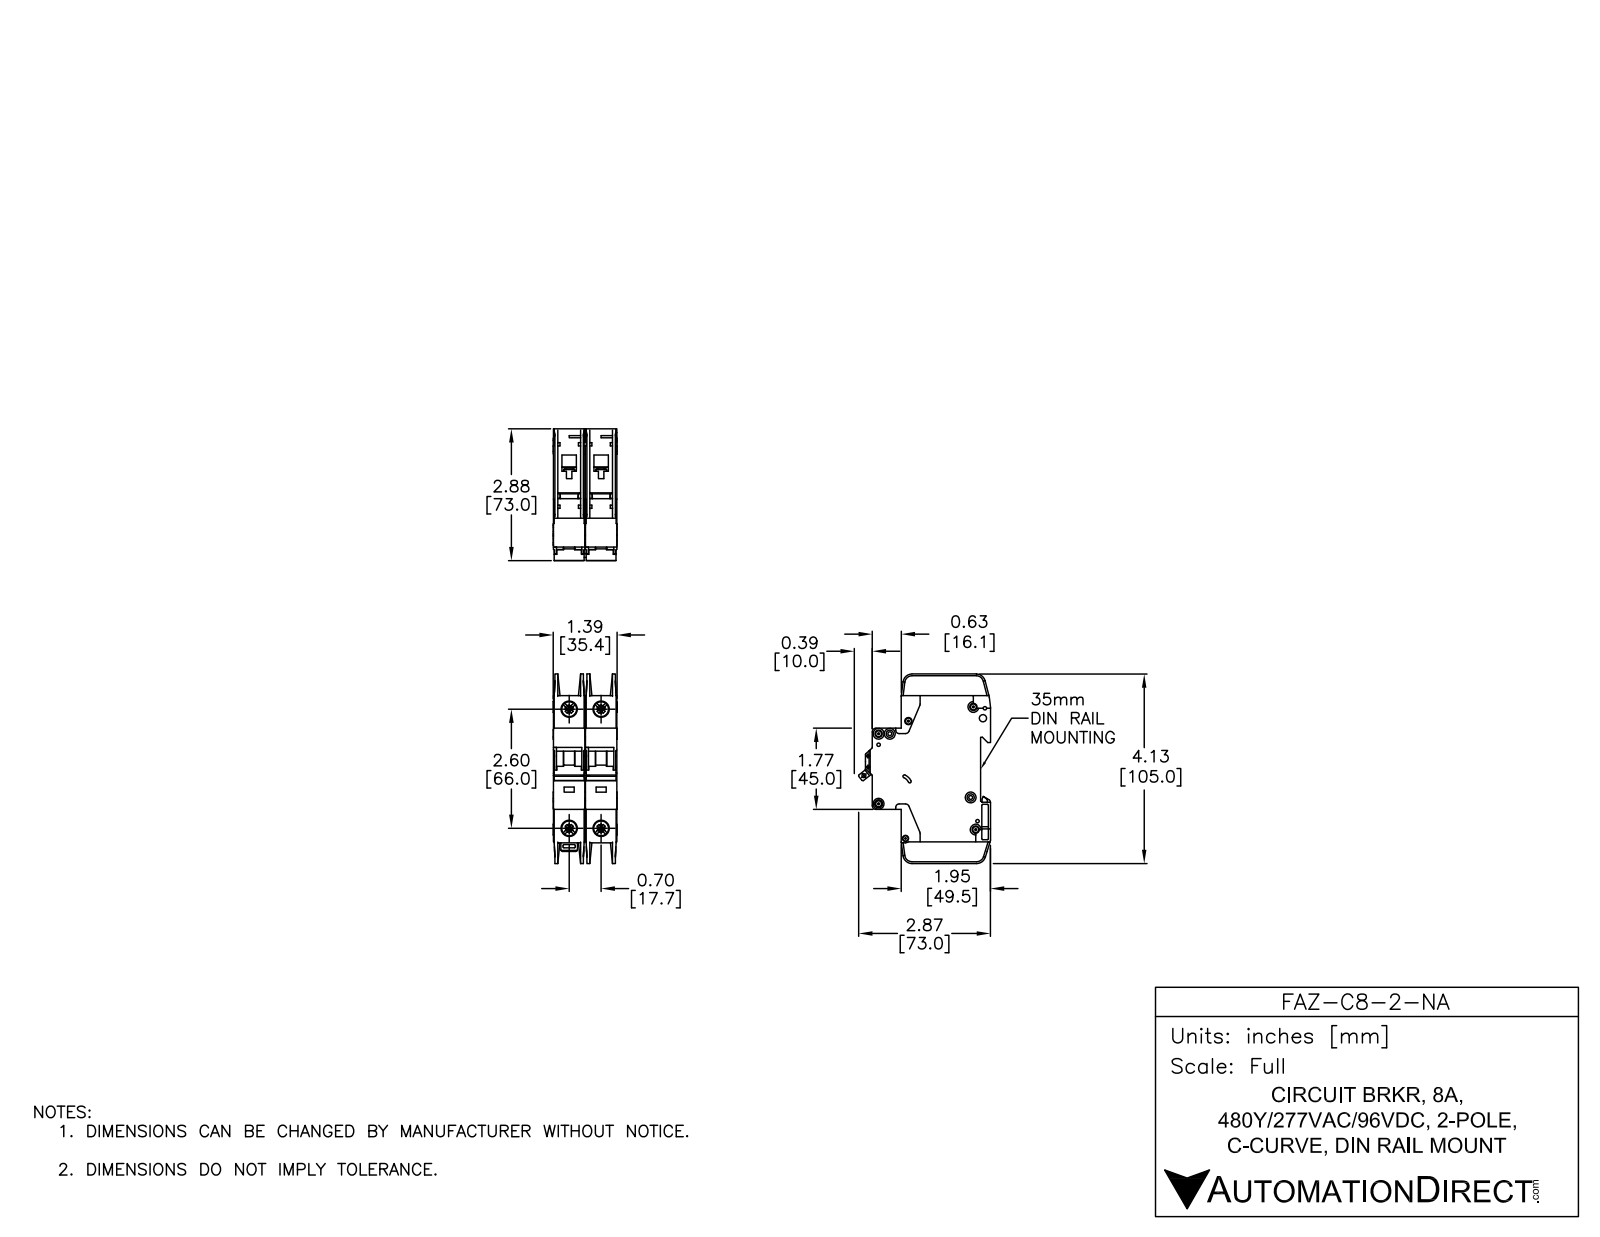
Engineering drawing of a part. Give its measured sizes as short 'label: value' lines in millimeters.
name: FAZ-C8-2-NA
written by: SolidWorks 2014 (AUTOMOTIVE_DESIGN)
unit: mm
bodies: 6 solids, 1568 faces (818 planar, 526 cylindrical, 224 other)
size: 105 × 73.04 × 35.4
volume: 155 390 mm³; area: 49 479 mm²
holes: 7× ⌀3.6, 4× ⌀7.15, 4× ⌀8.2, 2× ⌀1.09, 2× ⌀1.5, 2× ⌀4, 1× ⌀1.9, 1× ⌀2.15, 1× ⌀2.2, 1× ⌀2.55, 1× ⌀3.3, 1× ⌀3.4
bosses: 7× ⌀6, 2× ⌀2.5
rounds: 47× R0.25, 24× R0.5, 18× R1, 12× R2, 5× R5, 4× R1.8, 4× R4, 2× R0.2
face distances: 17.7, 17.5, 0.7, 15.05, 2.45, 1.75, 15.75, 13.3, 35.2, 17
hole spacings: 6.2, 17.7, 66, 68.33, 5.19, 6.1, 8.19, 8.56
